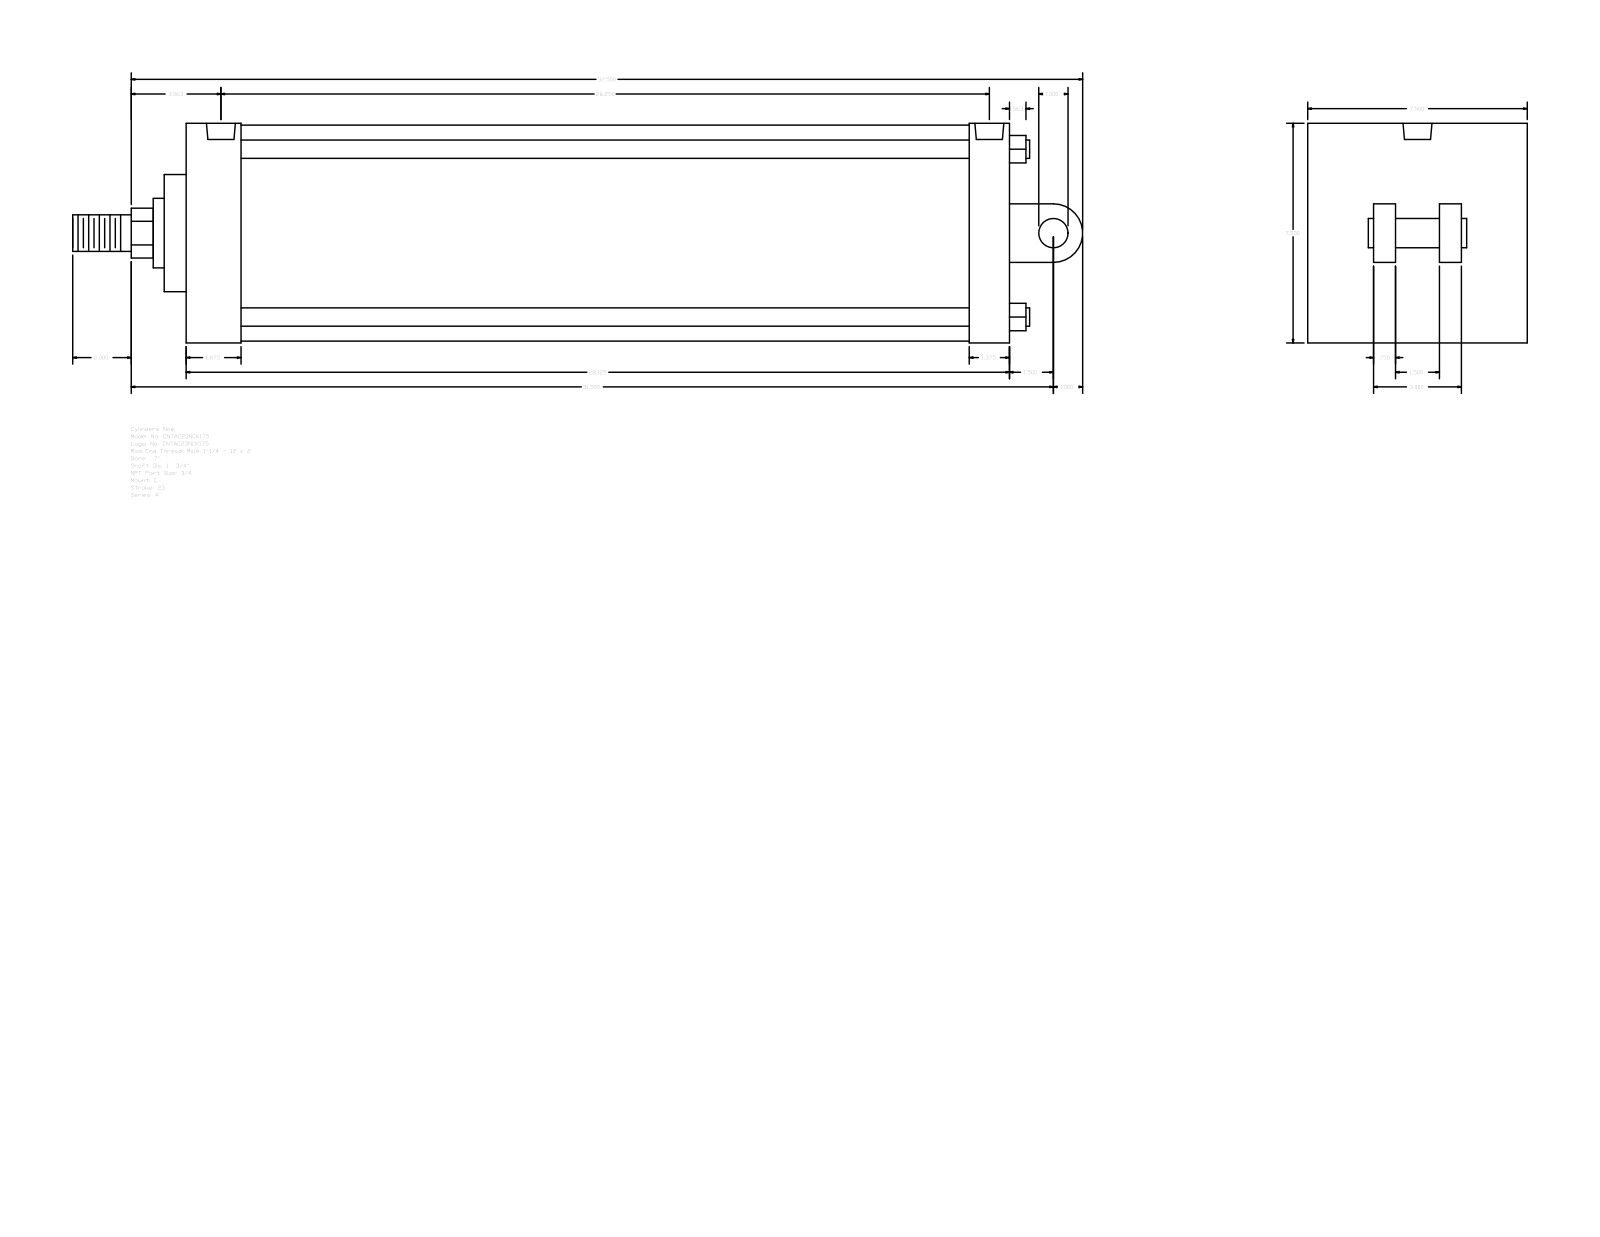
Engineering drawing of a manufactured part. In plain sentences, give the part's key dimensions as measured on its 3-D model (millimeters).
The part is named "A_C__0700_1.75". Its 3-D file was written by "GSSL Pune (CONFIG_CONTROL_DESIGN)". It is 0 solids with 104 faces: 75 planar, 29 cylindrical and 0 other. Overall it measures 876.3 by 190.5 by 190.5 millimeters. Round holes: 4 of diameter 15.08, 2 of diameter 25.12. Round bosses or shafts: 4 of diameter 15.88, 1 of diameter 187.32, 1 of diameter 60.33, 1 of diameter 44.45, 1 of diameter 31.75, 1 of diameter 25.4. Partial cylindrical surfaces (rounded edges, fillets, slot ends): 1 of radius 21.63, 1 of radius 25.4. The main face-to-face distances are 190.5, 714.38, 19.05, 76.2, 57.15, 146.05, 44.45, 69.85, 47.63, 666.75. The hole center spacings are 5.56, 655.63, 661.19, 666.75.
